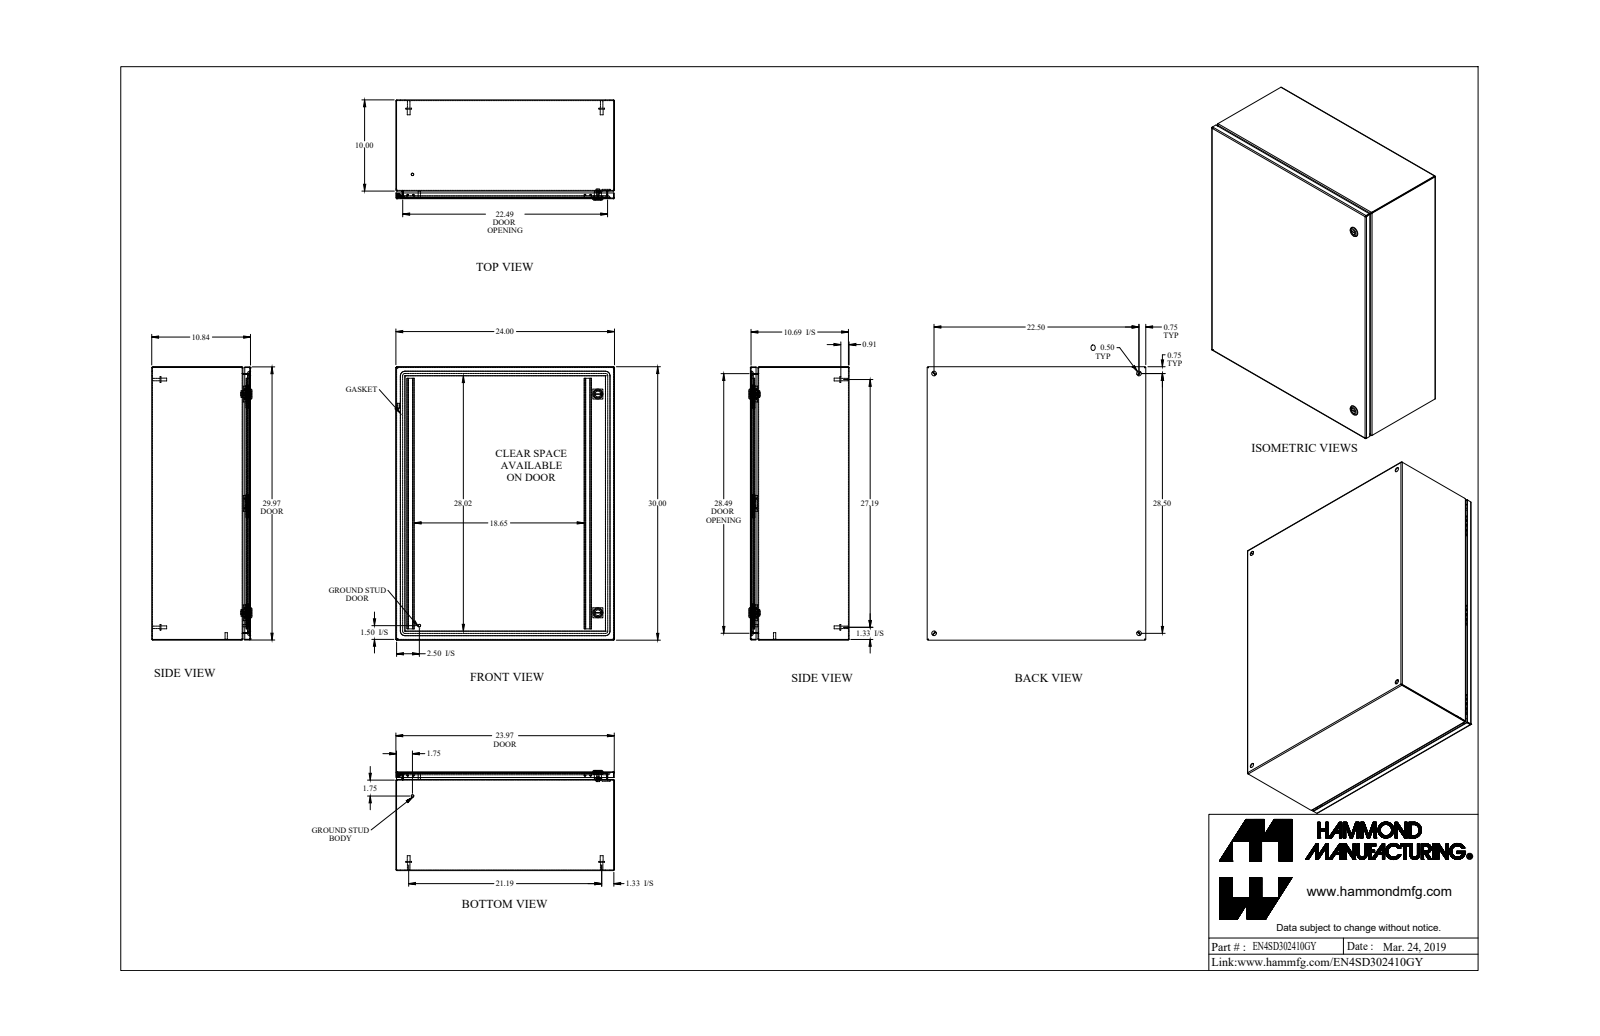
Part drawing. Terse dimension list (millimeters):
name: EN4SD302410GY
written by: SolidWorks 2019 (AUTOMOTIVE_DESIGN)
unit: mm
bodies: 31 solids, 854 faces (395 planar, 295 cylindrical, 164 other)
size: 762 × 609.6 × 279.3
volume: 3 456 000 mm³; area: 3 817 000 mm²
holes: 4× ⌀12.7, 2× ⌀5.9, 2× ⌀15.9, 2× ⌀19.9, 1× ⌀4.4, 1× ⌀6.1, 1× ⌀6.1
bosses: 4× ⌀15.9, 4× ⌀8, 4× ⌀6.9, 2× ⌀27.9, 2× ⌀13.3, 2× ⌀7.1, 2× ⌀6.4, 1× ⌀11.6
rounds: 16× R0.9, 16× R2.7, 12× R1.1, 12× R2.1, 12× R9.7, 8× R2.5, 8× R482.7, 6× R0.2
face distances: 1.8, 273.4, 271.6, 275.3, 607.8, 760.2, 605.9, 609.6, 758.3, 762
hole spacings: 571.5, 723.9, 922.3, 63.3, 63.3, 547.2, 547.2, 609.6
